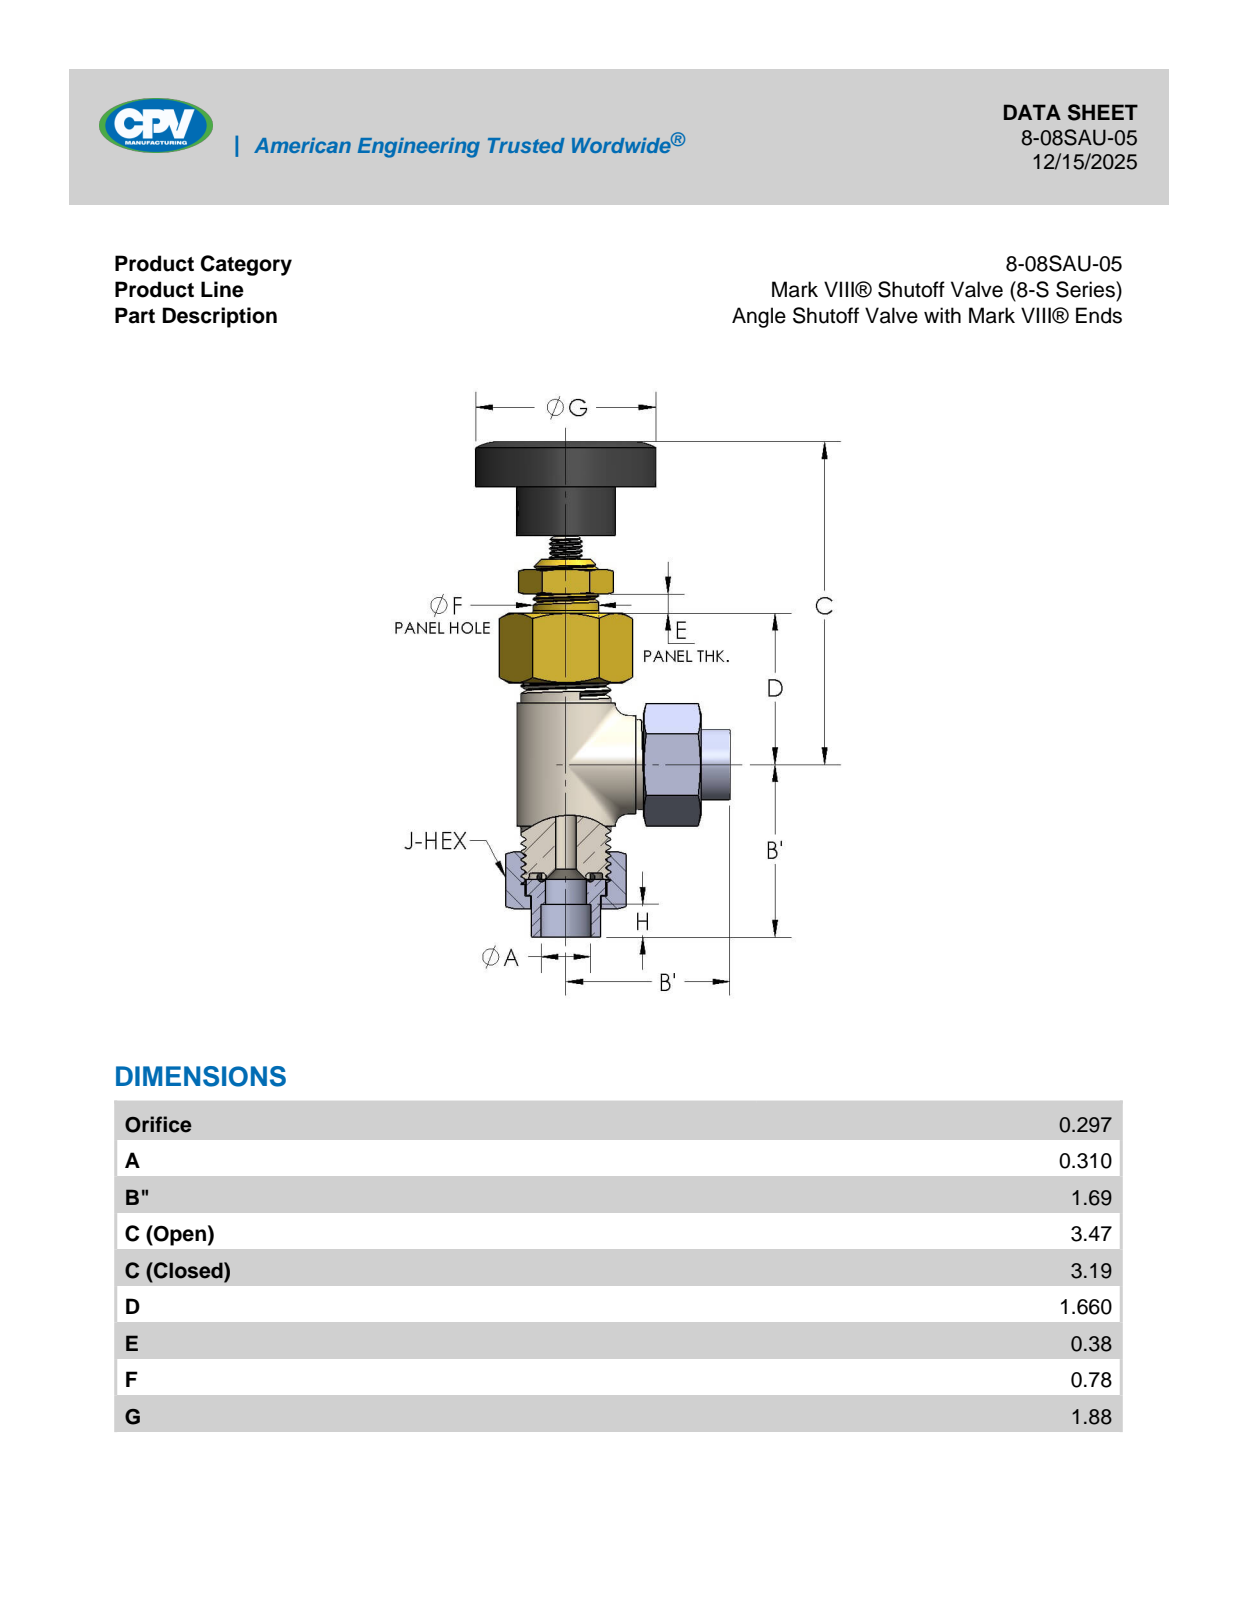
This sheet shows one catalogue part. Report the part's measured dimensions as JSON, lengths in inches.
{"part_name": "8-08SAU-05", "step_written_by": "SolidWorks 2018 (AUTOMOTIVE_DESIGN)", "units": "inches", "bodies": {"solids": 1, "faces": 178, "planar": 60, "cylindrical": 44, "other": 74}, "overall_size": [4.895, 2.628, 1.88], "volume_in3": 5.515, "surface_area_in2": 32.98, "round_holes": [[0.26, 2], [0.317, 2], [0.252, 1]], "round_bosses_or_shafts": [[0.808, 2], [0.469, 2], [1.88, 1], [1, 1], [0.996, 1], [0.748, 1], [0.312, 1], [0.25, 1]], "face_to_face_distances": [1.125, 0.31, 1.035, 0.5, 0.095, 0.093, 1.032, 1.128, 1.13, 0.095]}
